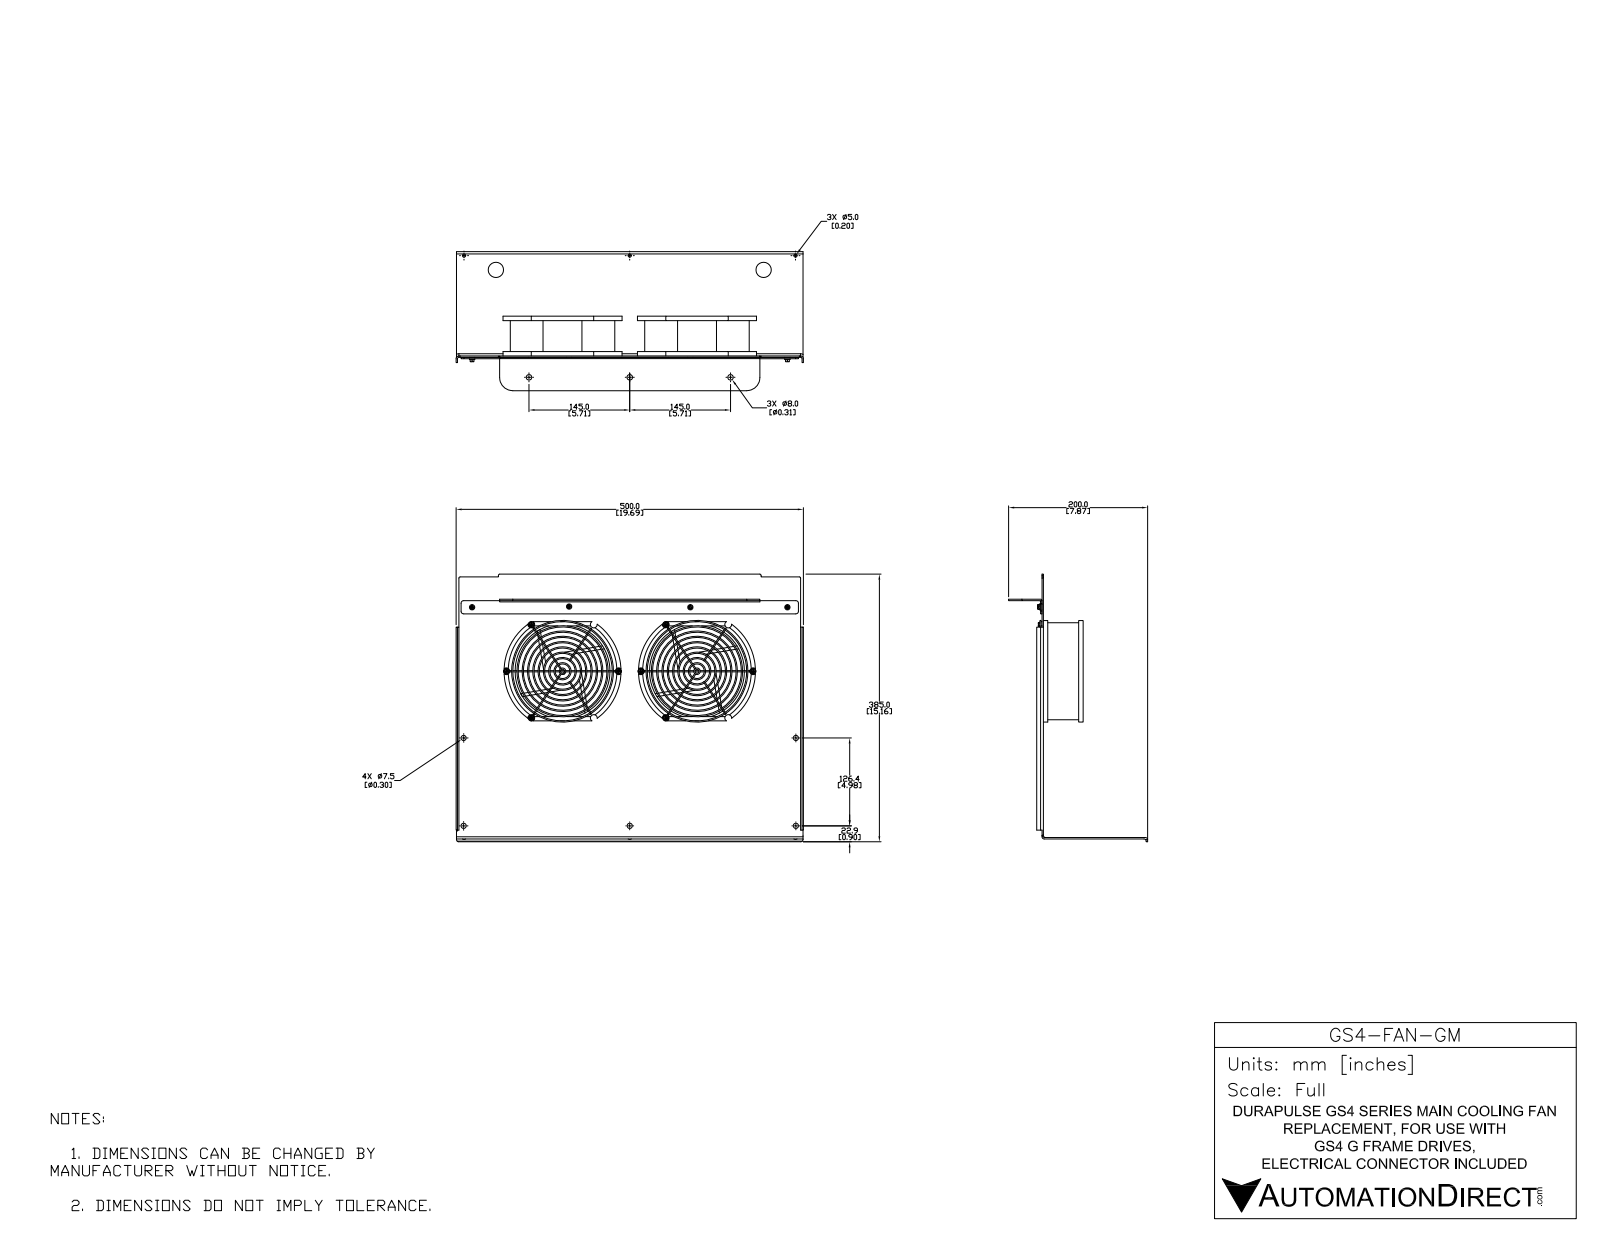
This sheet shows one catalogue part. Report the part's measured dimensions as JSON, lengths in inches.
{"part_name": "GS4-FAN-GM", "step_written_by": "SolidWorks 2016 (AUTOMOTIVE_DESIGN)", "units": "inches", "bodies": {"solids": 12, "faces": 680, "planar": 350, "cylindrical": 170, "other": 160}, "overall_size": [19.685, 15.157, 7.874], "volume_in3": 72.62, "surface_area_in2": 1163, "round_holes": [[0.2, 8], [0.295, 5], [0.197, 3], [0.313, 3], [0.865, 2]], "round_bosses_or_shafts": [[0.301, 12], [0.07, 1]], "partial_cylinders_radius": [[0.194, 12], [0.069, 6], [0.125, 6], [0.15, 4], [0.272, 4], [0.115, 2], [0.157, 2], [0.715, 2]], "face_to_face_distances": [0.079, 0.081, 0.08, 0.25, 0.181, 13.499, 13.58, 2, 13.419, 13.5], "hole_center_spacings": [3.005, 5.622, 7.62, 1.978, 3.756, 4.485, 4.976, 5.301]}
